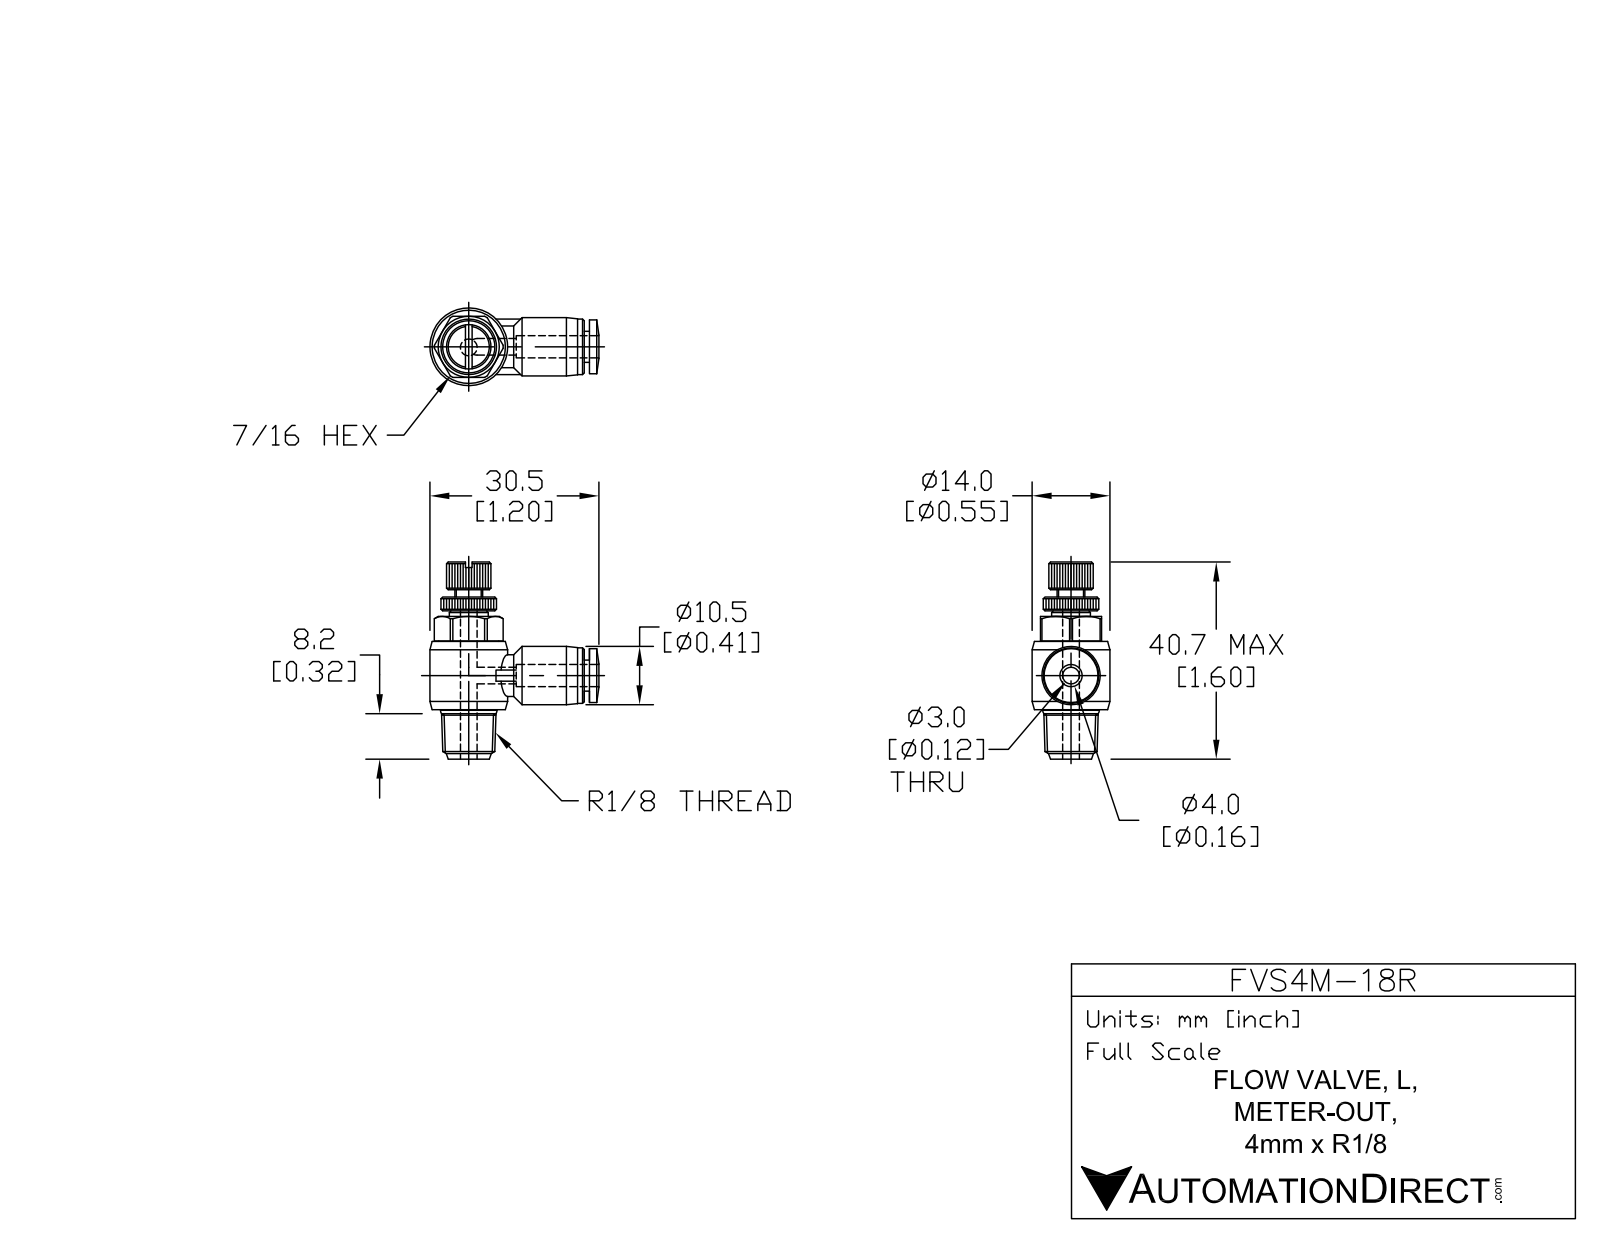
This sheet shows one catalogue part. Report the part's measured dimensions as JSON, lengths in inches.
{"part_name": "FVS4M-18R", "step_written_by": "SolidWorks 2015 (AUTOMOTIVE_DESIGN)", "units": "inches", "bodies": {"solids": 1, "faces": 492, "planar": 189, "cylindrical": 113, "other": 190}, "overall_size": [1.602, 1.199, 0.551], "volume_in3": 0.269, "surface_area_in2": 4.426, "round_holes": [[0.118, 2], [0.169, 1]], "round_bosses_or_shafts": [[0.382, 2], [0.551, 1], [0.425, 1], [0.413, 1], [0.394, 1], [0.295, 1], [0.276, 1], [0.22, 1]], "partial_cylinders_radius": [[0.157, 1], [0.197, 1], [0.244, 1]], "face_to_face_distances": [0.433, 0.661, 0.206, 0.799, 0.138, 0.039, 0.484, 0.177, 0.315, 0.037]}
